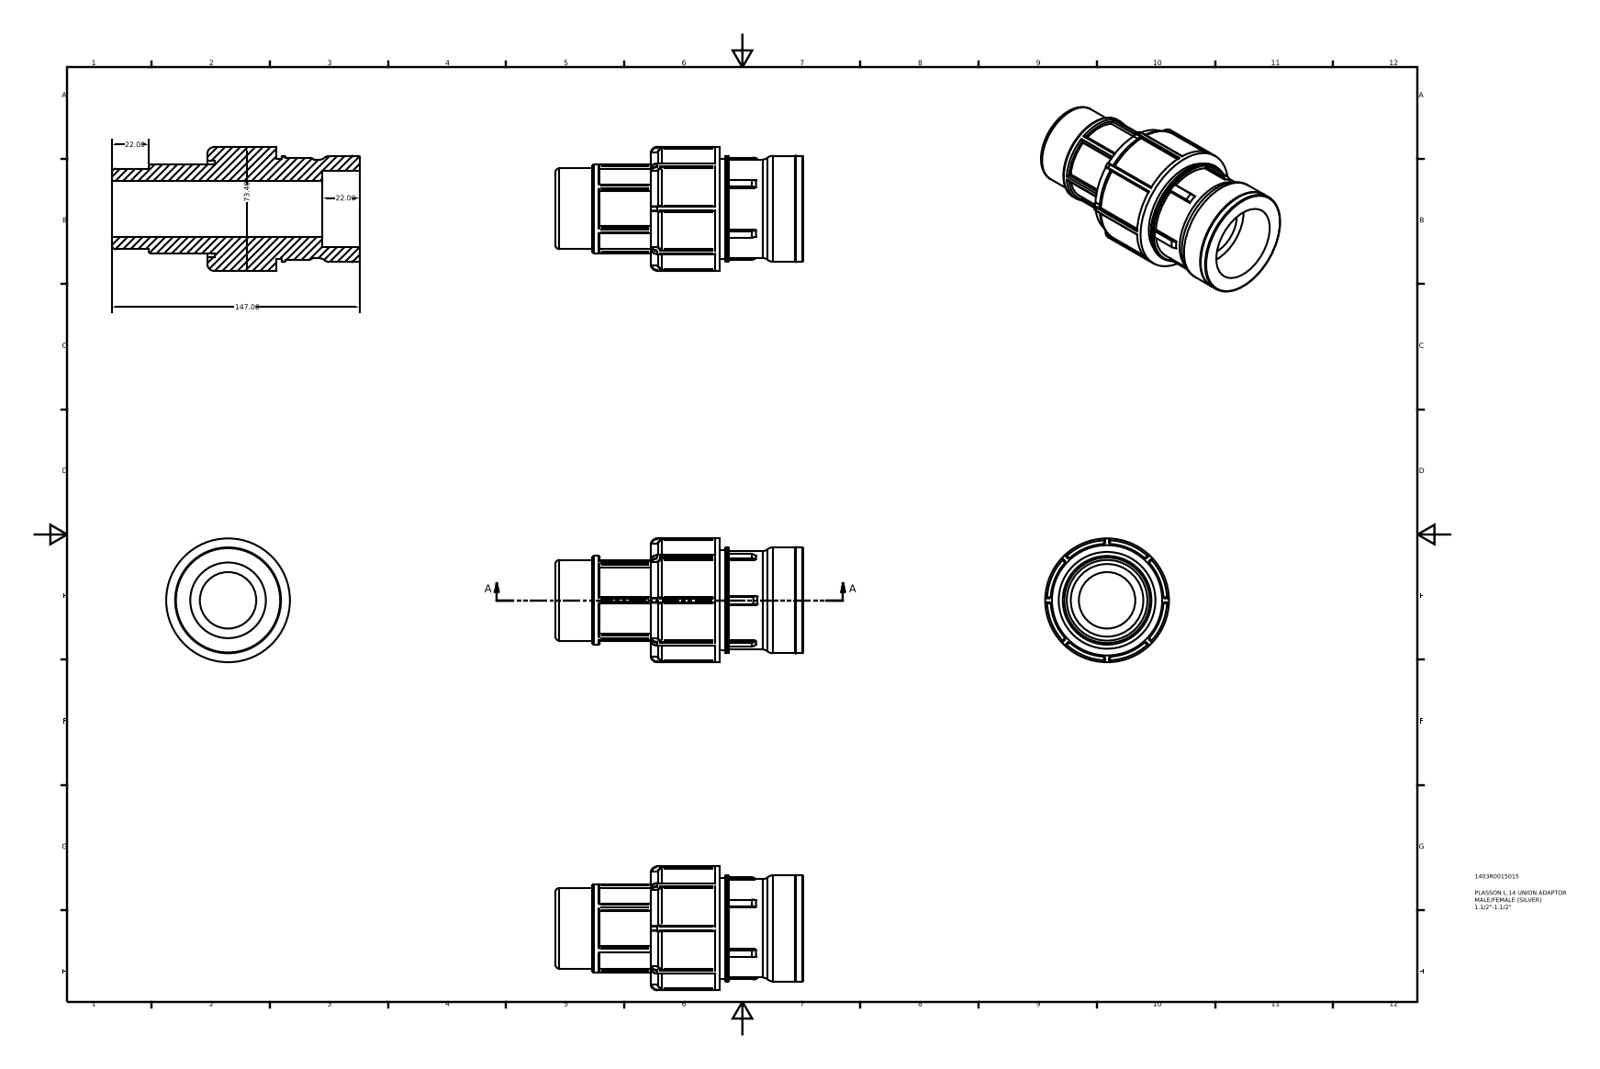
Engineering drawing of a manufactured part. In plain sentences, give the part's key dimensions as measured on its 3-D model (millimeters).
The part is named "1403R0015015". Its 3-D file was written by "Autodesk Inventor 2015 (AUTOMOTIVE_DESIGN)". It is 1 solid with 220 faces: 69 planar, 94 cylindrical and 57 other. Overall it measures 147 by 73.4 by 73.4 millimeters. Its volume is 262 304 cubic millimeters and its surface area 54 283 square millimeters. Round holes: 1 of diameter 33.46, 1 of diameter 44.84, 1 of diameter 57.36. Round bosses or shafts: 1 of diameter 73.4, 1 of diameter 71.2, 1 of diameter 66.92, 1 of diameter 62.78, 1 of diameter 59.64, 1 of diameter 58.3, 1 of diameter 52.58, 1 of diameter 47.8. Partial cylindrical surfaces (rounded edges, fillets, slot ends): 32 of radius 0.37, 12 of radius 0.45, 12 of radius 0.96, 5 of radius 3.67. The main face-to-face distances are 49.24, 22, 68.41, 125, 41.17, 90.41, 4.41, 36.76, 86, 64.
